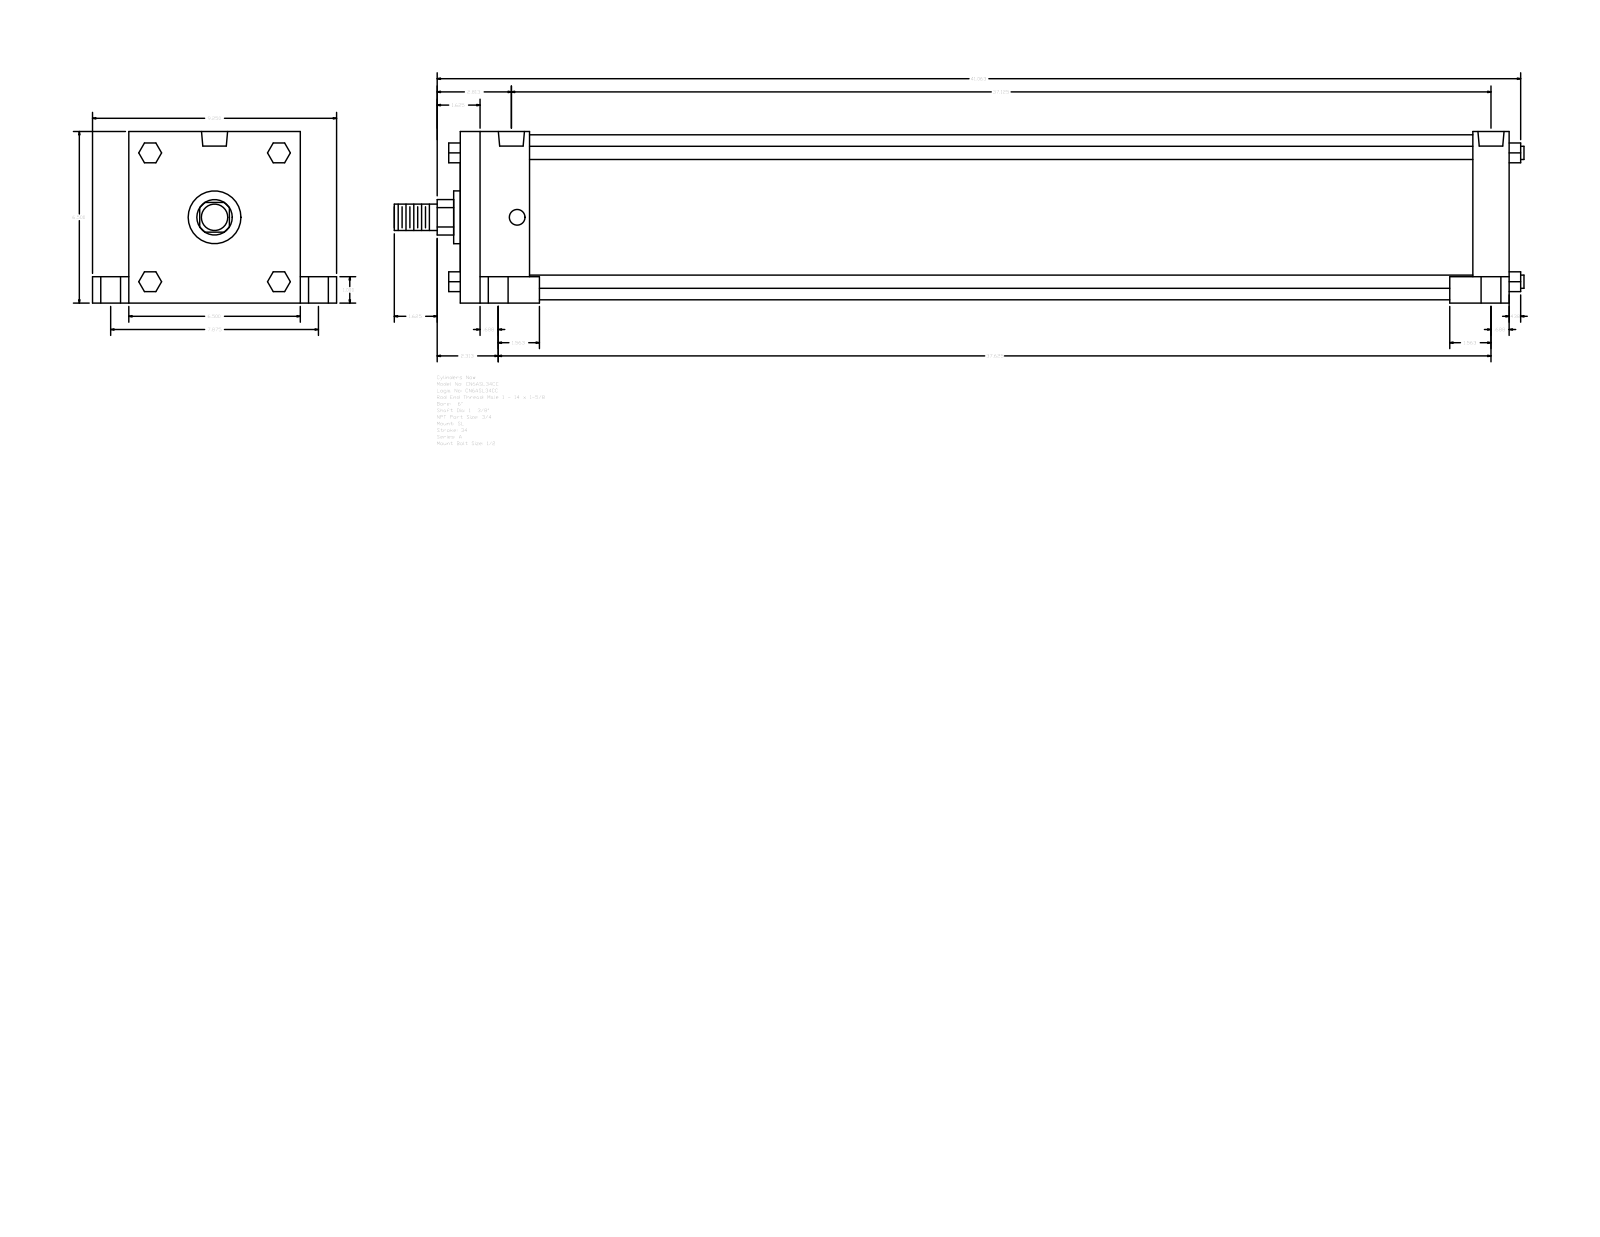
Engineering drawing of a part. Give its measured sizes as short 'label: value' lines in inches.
name: A_SL__0600_1.375
written by: GSSL Pune (CONFIG_CONTROL_DESIGN)
unit: in
bodies: 0 solids, 150 faces (114 planar, 36 cylindrical, 0 other)
size: 42.813 × 9.25 × 6.5
holes: 4× ⌀0.594, 4× ⌀0.75, 4× ⌀1, 2× ⌀0.989
bosses: 4× ⌀0.5, 1× ⌀6.25, 1× ⌀2, 1× ⌀1.375, 1× ⌀1
rounds: 1× R0.672
face distances: 6.5, 39.75, 2.625, 37.125, 38.375, 35.75, 1.375, 1, 5.5, 1.375
hole spacings: 0.219, 3.937, 3.943, 3.969, 4.002, 7.875, 36.687, 36.906
